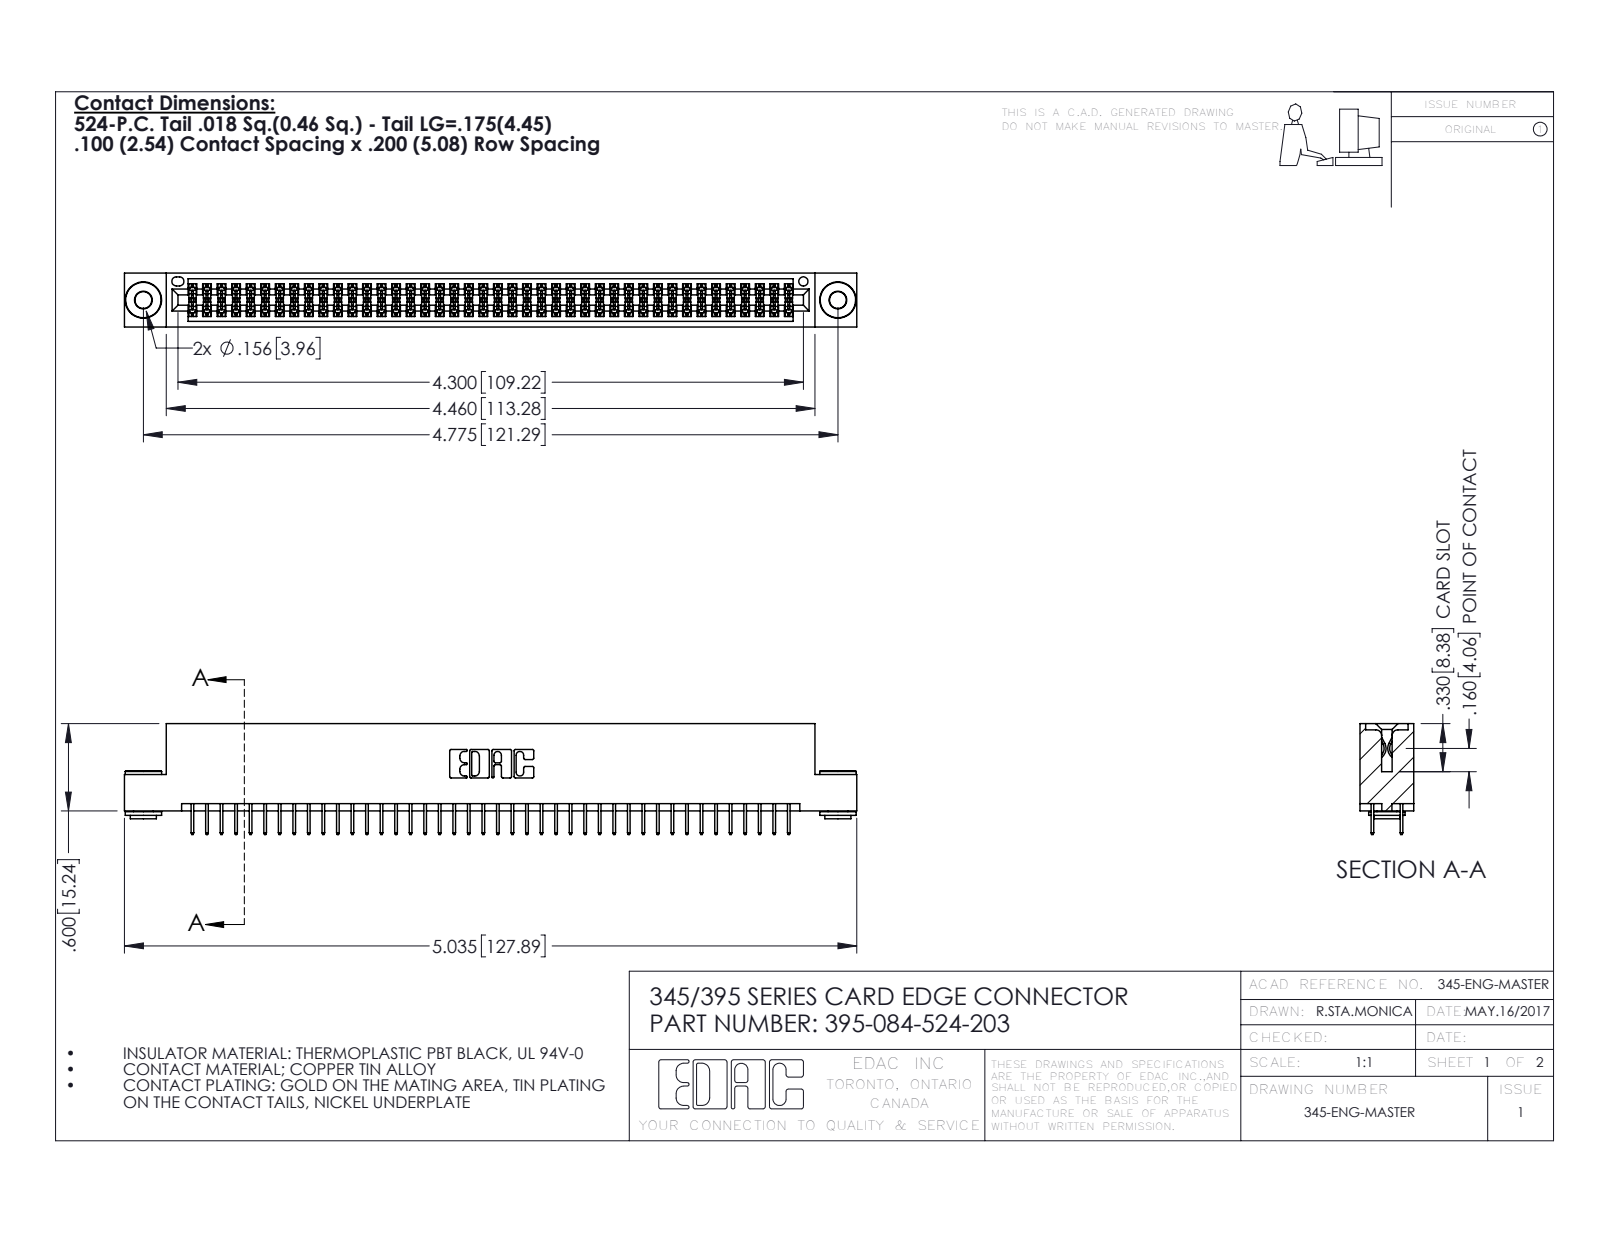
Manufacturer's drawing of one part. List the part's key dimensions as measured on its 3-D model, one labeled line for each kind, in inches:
Part name (STEP PRODUCT): 345 Part_Flush Mounting Lugs - 0.156 Dia-TH; 395-084-524-203; 345-250-002_345-250-002-102; 345-292-001_345-293-124
STEP written by: SolidWorks 2016 (CONFIG_CONTROL_DESIGN)
Units: inches
Bodies: 87 solids, 4700 faces (3366 planar, 1326 cylindrical, 8 other)
Overall size (bounding box): 5.035 × 0.762 × 0.37
Volume: 0.752 in³ · Surface area: 28.01 in²
Round holes (diameter × count): ⌀0.116 ×2, ⌀0.156 ×2, ⌀0.064 ×1
Round bosses / shafts (diameter × count): ⌀0.25 ×2, ⌀0.18 ×2, ⌀0.136 ×2
Partial cylindrical surfaces — rounded edges, fillets, slot ends (radius × count): R0.006 ×126, R0.01 ×22, R0.007 ×6, R0.031 ×6, R0.026 ×3, R0.014 ×2, R0.019 ×2, R0.022 ×2
Main face-to-face distances: 0.072, 0.298, 0.2, 0.37, 0.025, 0.098, 0.272, 0.225, 0.072, 0.175
Hole centre spacings: 0.27, 4.539, 4.775
